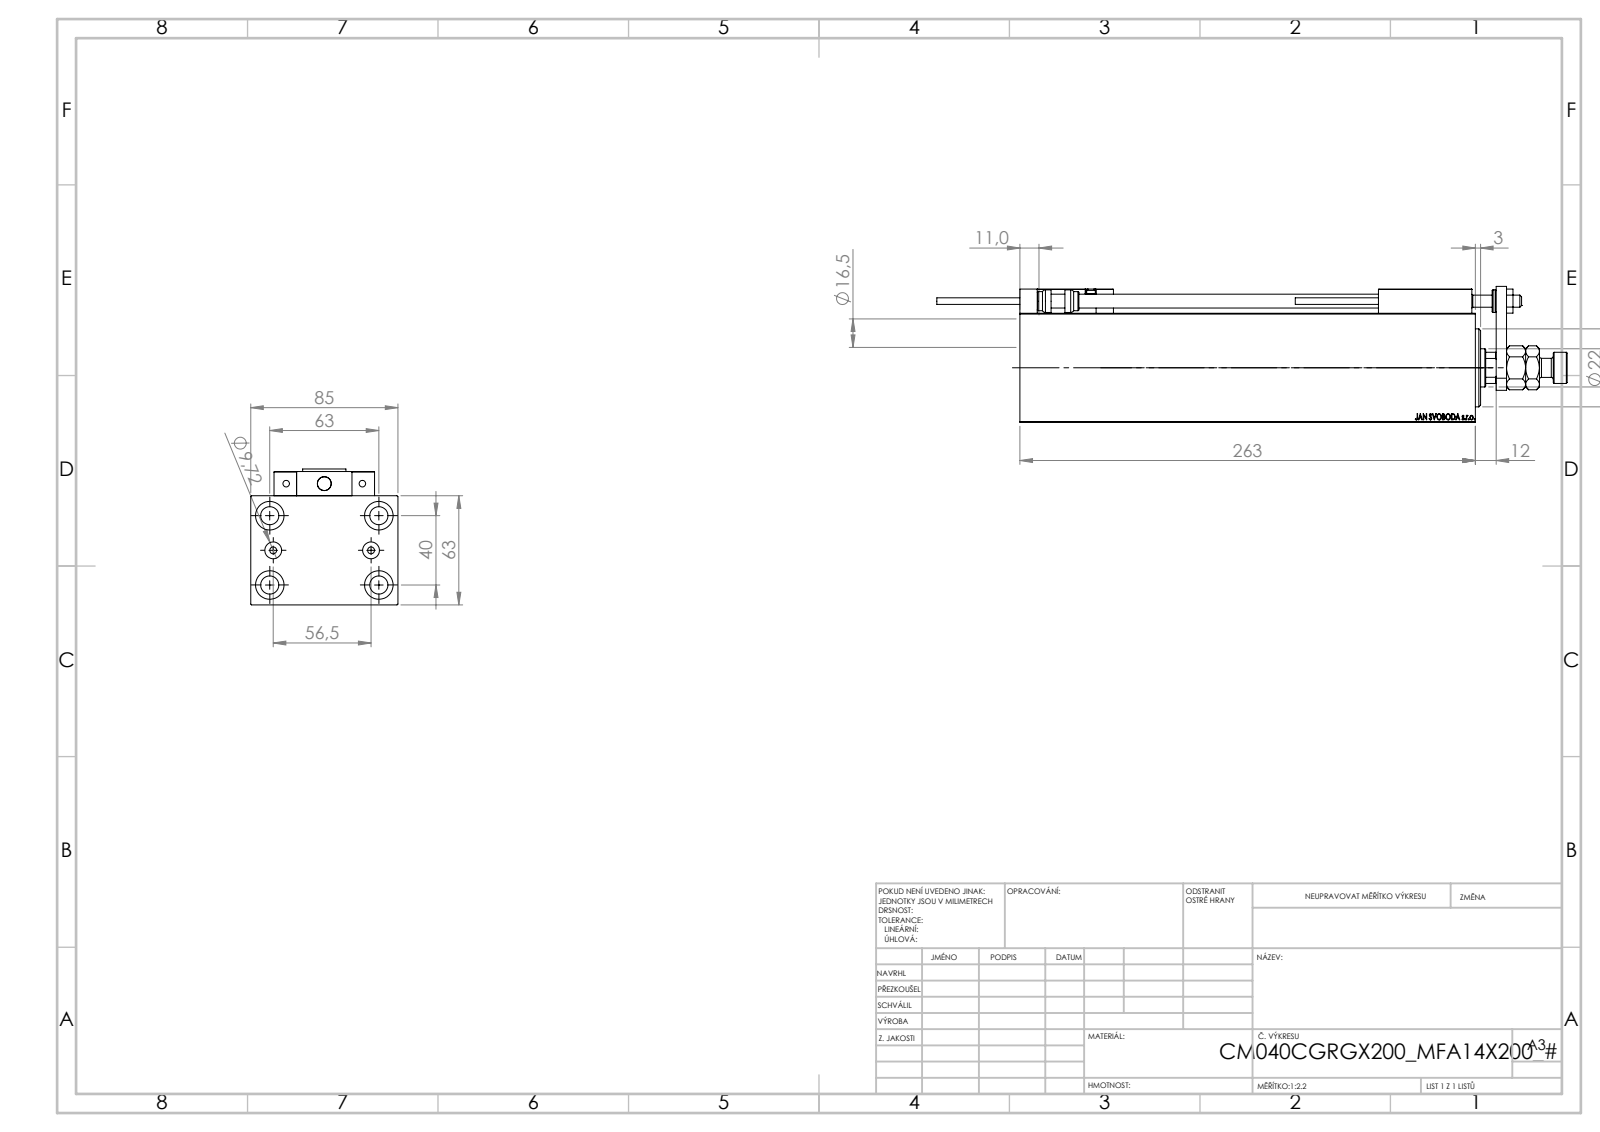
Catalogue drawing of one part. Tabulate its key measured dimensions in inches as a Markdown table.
| quantity | value |
| --- | --- |
| part name | ALLEN BOLT D8; SWITCH_X_FRONT_BACK; X_Y_MFA; KONCOVKA (+7 more) |
| STEP written by | SolidWorks 2019 (CONFIG_CONTROL_DESIGN) |
| units | inches |
| bodies | 24 solids, 1330 faces (576 planar, 188 cylindrical, 566 other) |
| overall size | 14.331 × 3.346 × 3.091 |
| volume | 72.98 in³ |
| surface area | 346.9 in² |
| round holes (diameter × count) | 0.157 × 6, 0.315 × 5, 0.65 × 5, 0.126 × 4, 0.413 × 4, 0.197 × 2, 0.383 × 2, 0.276 × 1, 0.492 × 1, 0.866 × 1, 1.004 × 1, 1.575 × 1 |
| round bosses / shafts (diameter × count) | 0.433 × 2, 0.197 × 2, 0.15 × 2, 0.709 × 1, 0.512 × 1 |
| partial cylindrical surfaces (radius × count) | 0.012 × 30, 0.118 × 2, 0.413 × 1 |
| main face-to-face distances | 2.48, 3.346, 0.472, 9.882, 10.354, 0.551, 0.709, 1.181, 3.031, 0.787 |
| hole center spacings | 1.469, 0.448, 0.787, 0.791, 0.807, 1.165, 1.169, 1.42 |
